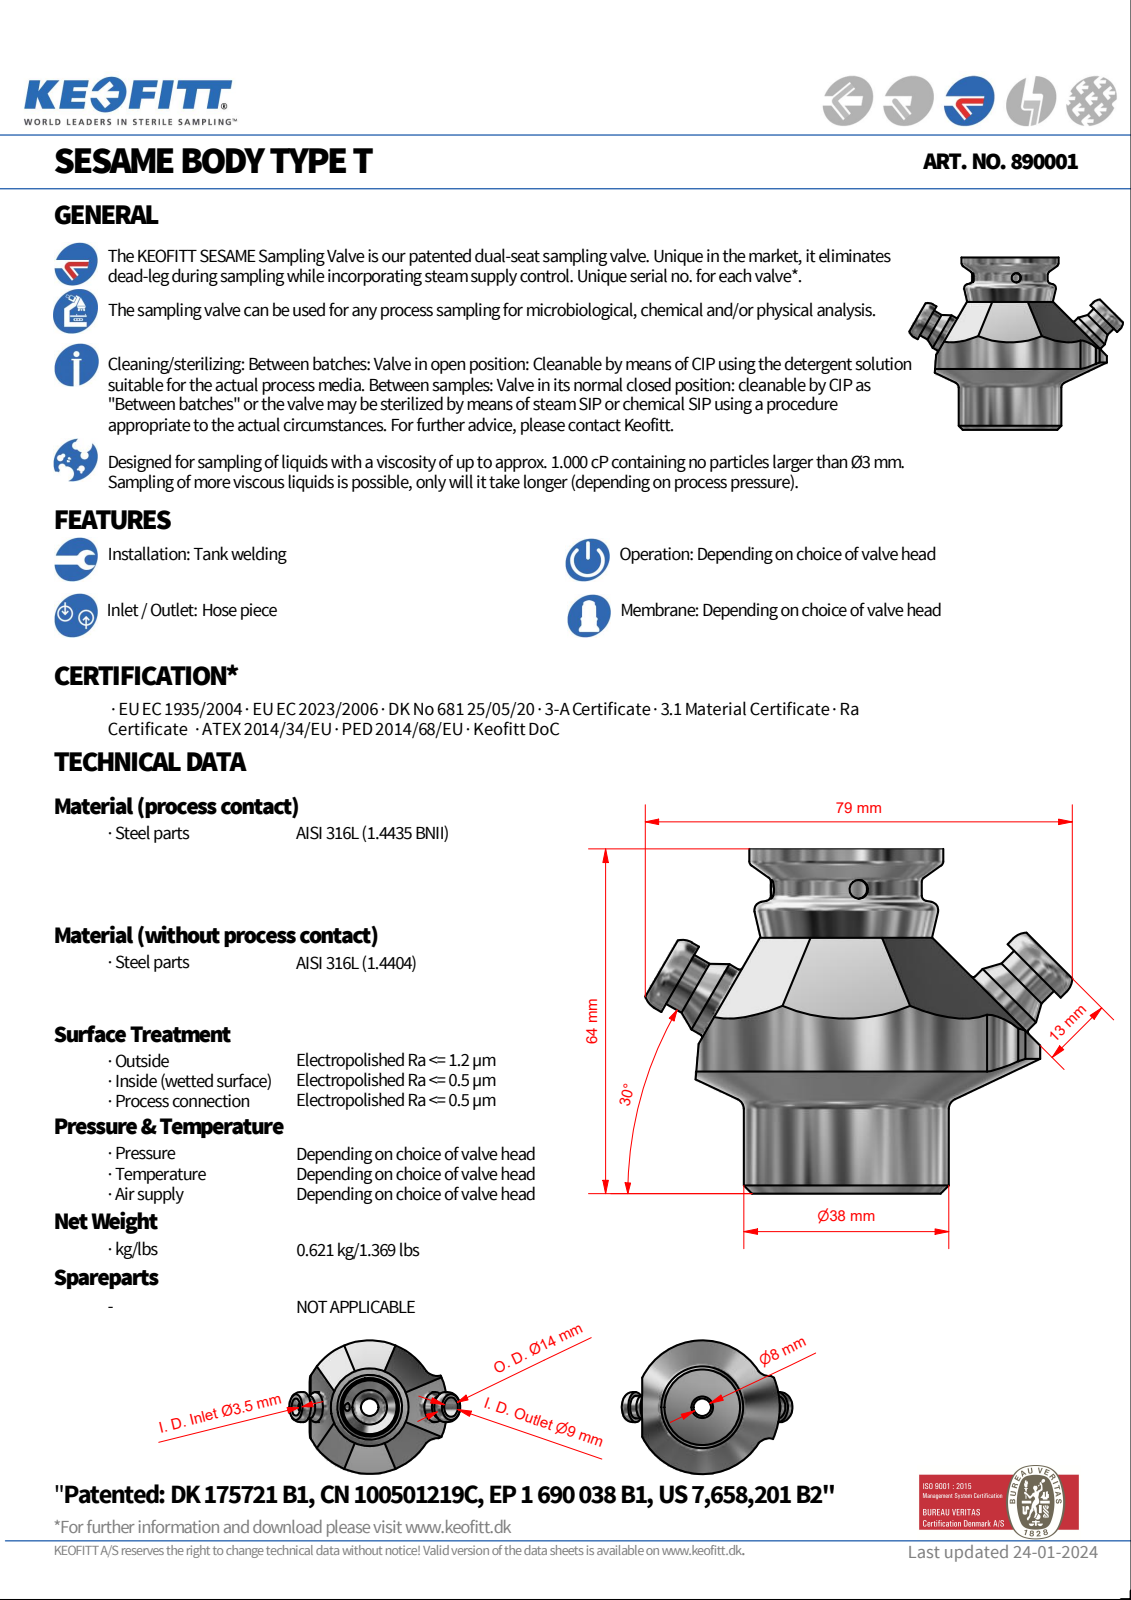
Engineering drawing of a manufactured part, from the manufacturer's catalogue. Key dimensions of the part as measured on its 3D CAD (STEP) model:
Part name (STEP PRODUCT): 890001
STEP written by: Autodesk Inventor 2020 (AUTOMOTIVE_DESIGN)
Units: millimetres
Bodies: 1 solid, 77 faces (23 planar, 32 cylindrical, 22 other)
Overall size (bounding box): 79.23 × 64 × 62
Volume: 95 310 mm³ · Surface area: 17 572 mm²
Round holes (diameter × count): ⌀3.5 ×3, ⌀9 ×1, ⌀26 ×1, ⌀29 ×1, ⌀30 ×1
Round bosses / shafts (diameter × count): ⌀14 ×3, ⌀10.5 ×2, ⌀38 ×1, ⌀36 ×1, ⌀28.7 ×1, ⌀28.5 ×1, ⌀28 ×1, ⌀27.34 ×1
Partial cylindrical surfaces — rounded edges, fillets, slot ends (radius × count): R7 ×2, R31 ×1, R36 ×1
Main face-to-face distances: 53, 64, 11, 61, 8, 3, 47.5, 5.5, 13.5, 16.5
